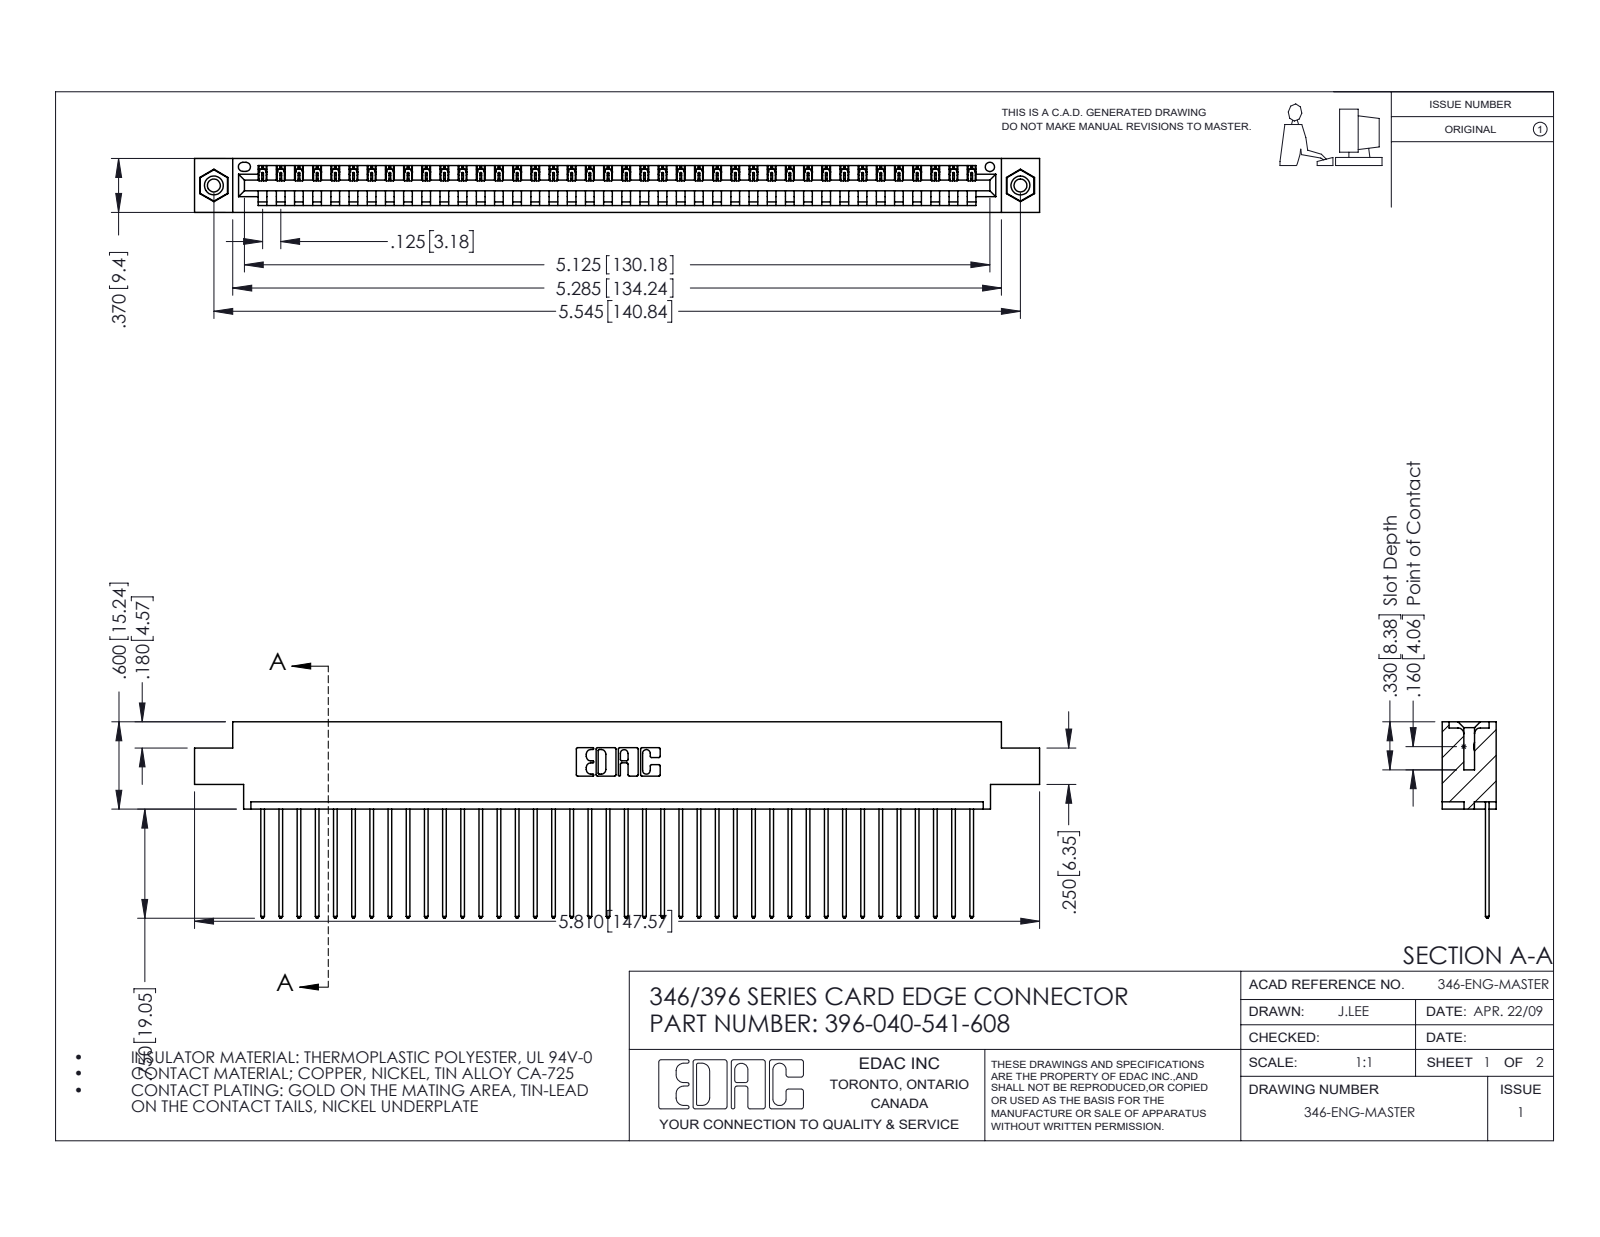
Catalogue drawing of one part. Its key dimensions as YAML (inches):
part_name: "345-250-001_345-250-003-102; 346 Part_0.170 Offset - 0.156 Dia-TI; 345-292-001_345-293-141; 396-040-541-608"
step_written_by: "SolidWorks 2016 (CONFIG_CONTROL_DESIGN)"
units: inches
bodies: {solids: 43, faces: 2506, planar: 1712, cylindrical: 778, other: 16}
overall_size: [5.81, 1.35, 0.37]
volume: 0.859
surface_area: 28.75
round_holes:
  - {diameter: 0.089, count: 2}
  - {diameter: 0.125, count: 2}
  - {diameter: 0.156, count: 2}
  - {diameter: 0.064, count: 1}
round_bosses_or_shafts:
  - {diameter: 0.155, count: 2}
partial_cylinders:
  - {radius: 0.006, count: 80}
  - {radius: 0.01, count: 80}
  - {radius: 0.01, count: 22}
  - {radius: 0.007, count: 6}
  - {radius: 0.031, count: 6}
  - {radius: 0.026, count: 3}
  - {radius: 0.031, count: 2}
  - {radius: 0.04, count: 2}
face_to_face_distances: [0.048, 0.322, 0.37, 0.25, 0.072, 0.298, 0.025, 0.222, 0.148, 0.1]
hole_center_spacings: [0.246, 5.336, 5.545]
